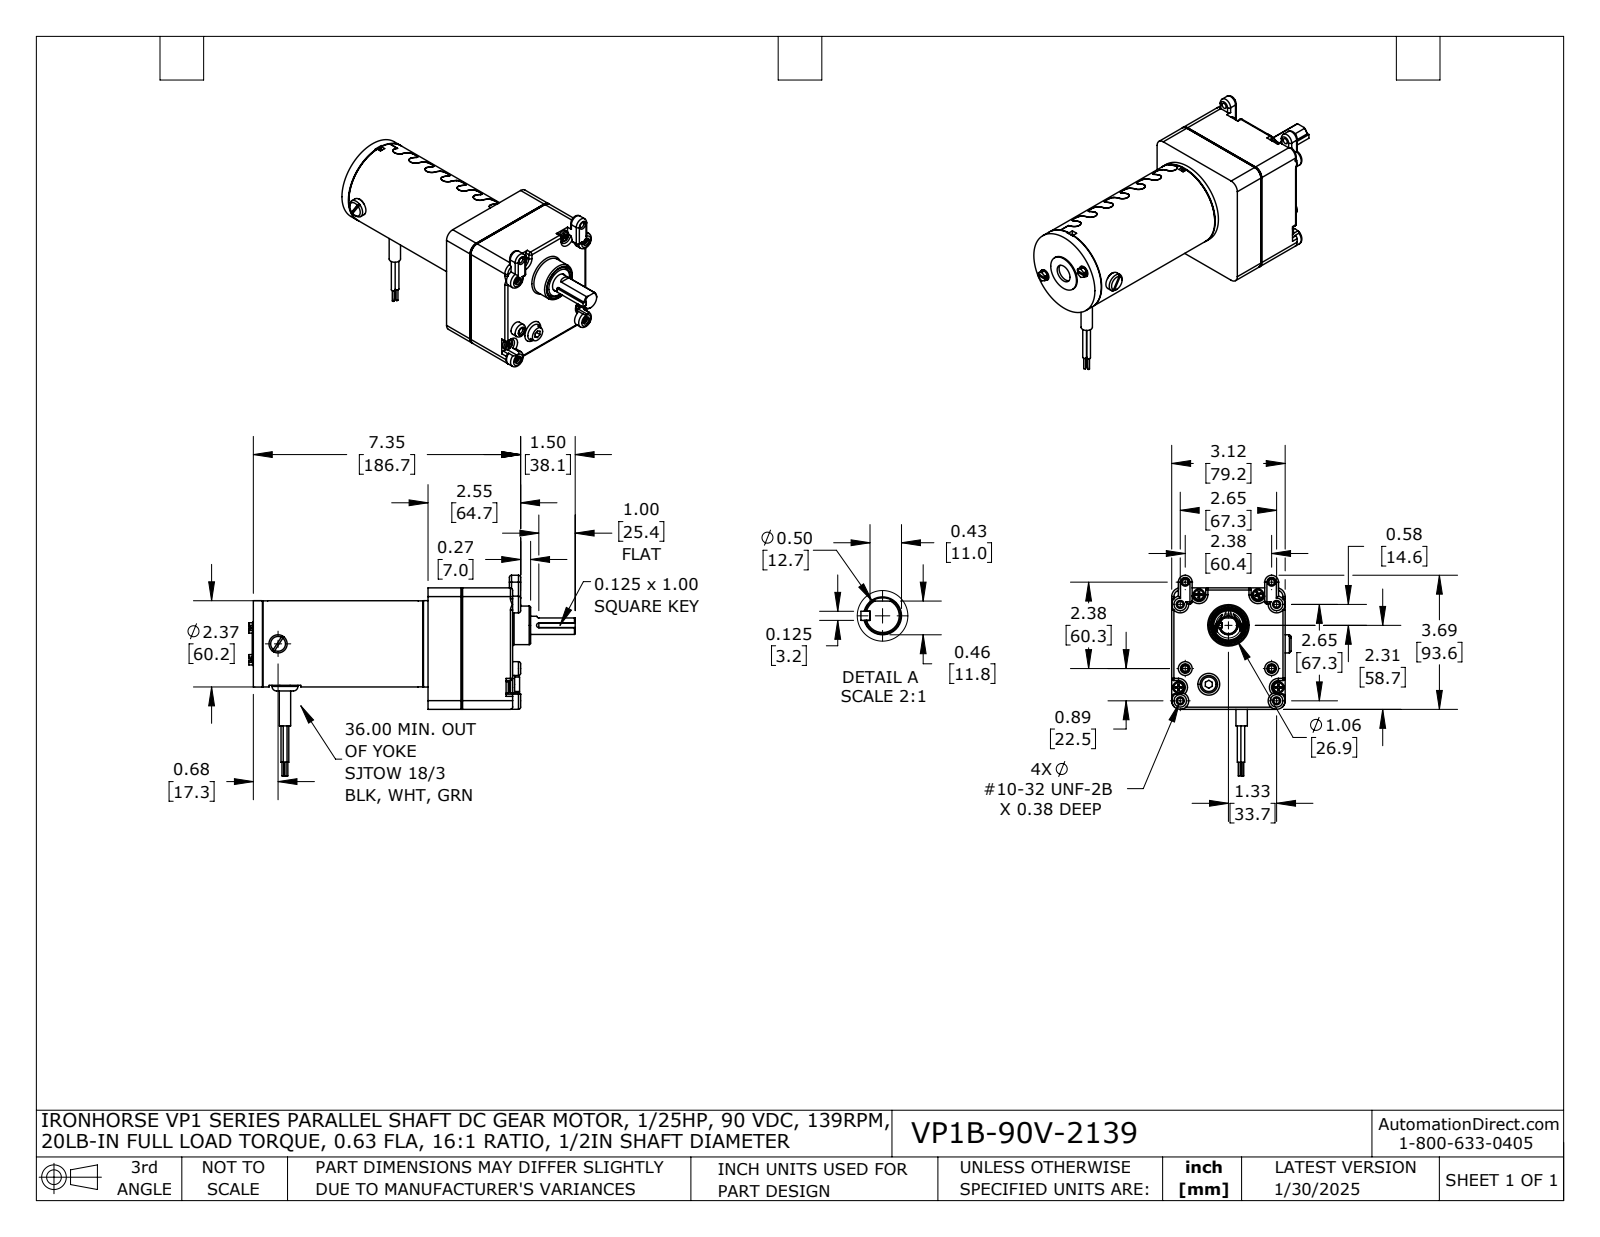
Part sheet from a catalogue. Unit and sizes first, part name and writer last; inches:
Units: inches
Overall size (bounding box): 8.974 × 5.516 × 3.283
Round holes (diameter × count): ⌀0.2 ×11, ⌀0.158 ×8, ⌀0.18 ×4, ⌀0.187 ×2, ⌀0.189 ×2, ⌀0.22 ×2, ⌀0.213 ×1, ⌀0.336 ×1, ⌀0.468 ×1, ⌀0.5 ×1, ⌀0.521 ×1, ⌀0.688 ×1
Round bosses / shafts (diameter × count): ⌀0.314 ×4, ⌀0.313 ×4, ⌀0.136 ×4, ⌀0.105 ×3, ⌀0.052 ×3, ⌀0.5 ×2, ⌀0.466 ×2, ⌀0.44 ×2
Partial cylindrical surfaces — rounded edges, fillets, slot ends (radius × count): R0.06 ×34, R0.062 ×21, R0.156 ×14, R0.151 ×7, R0.161 ×7, R0.15 ×6, R0.12 ×4, R0.235 ×4
Main face-to-face distances: 0.09, 3.12, 1.38, 2.326, 0.946, 0.106, 1.274, 2.22, 3.34, 0.315
Hole centre spacings: 1.68, 2.65, 1.074, 2.729, 3.093, 0.077, 0.297, 0.373
Volume: 12.28 in³ · Surface area: 225.5 in²
Bodies: 20 solids, 916 faces (340 planar, 422 cylindrical, 154 other)
Part name (STEP PRODUCT): VP1B-90V-2139
STEP written by: SolidWorks 2021 (AUTOMOTIVE_DESIGN)
